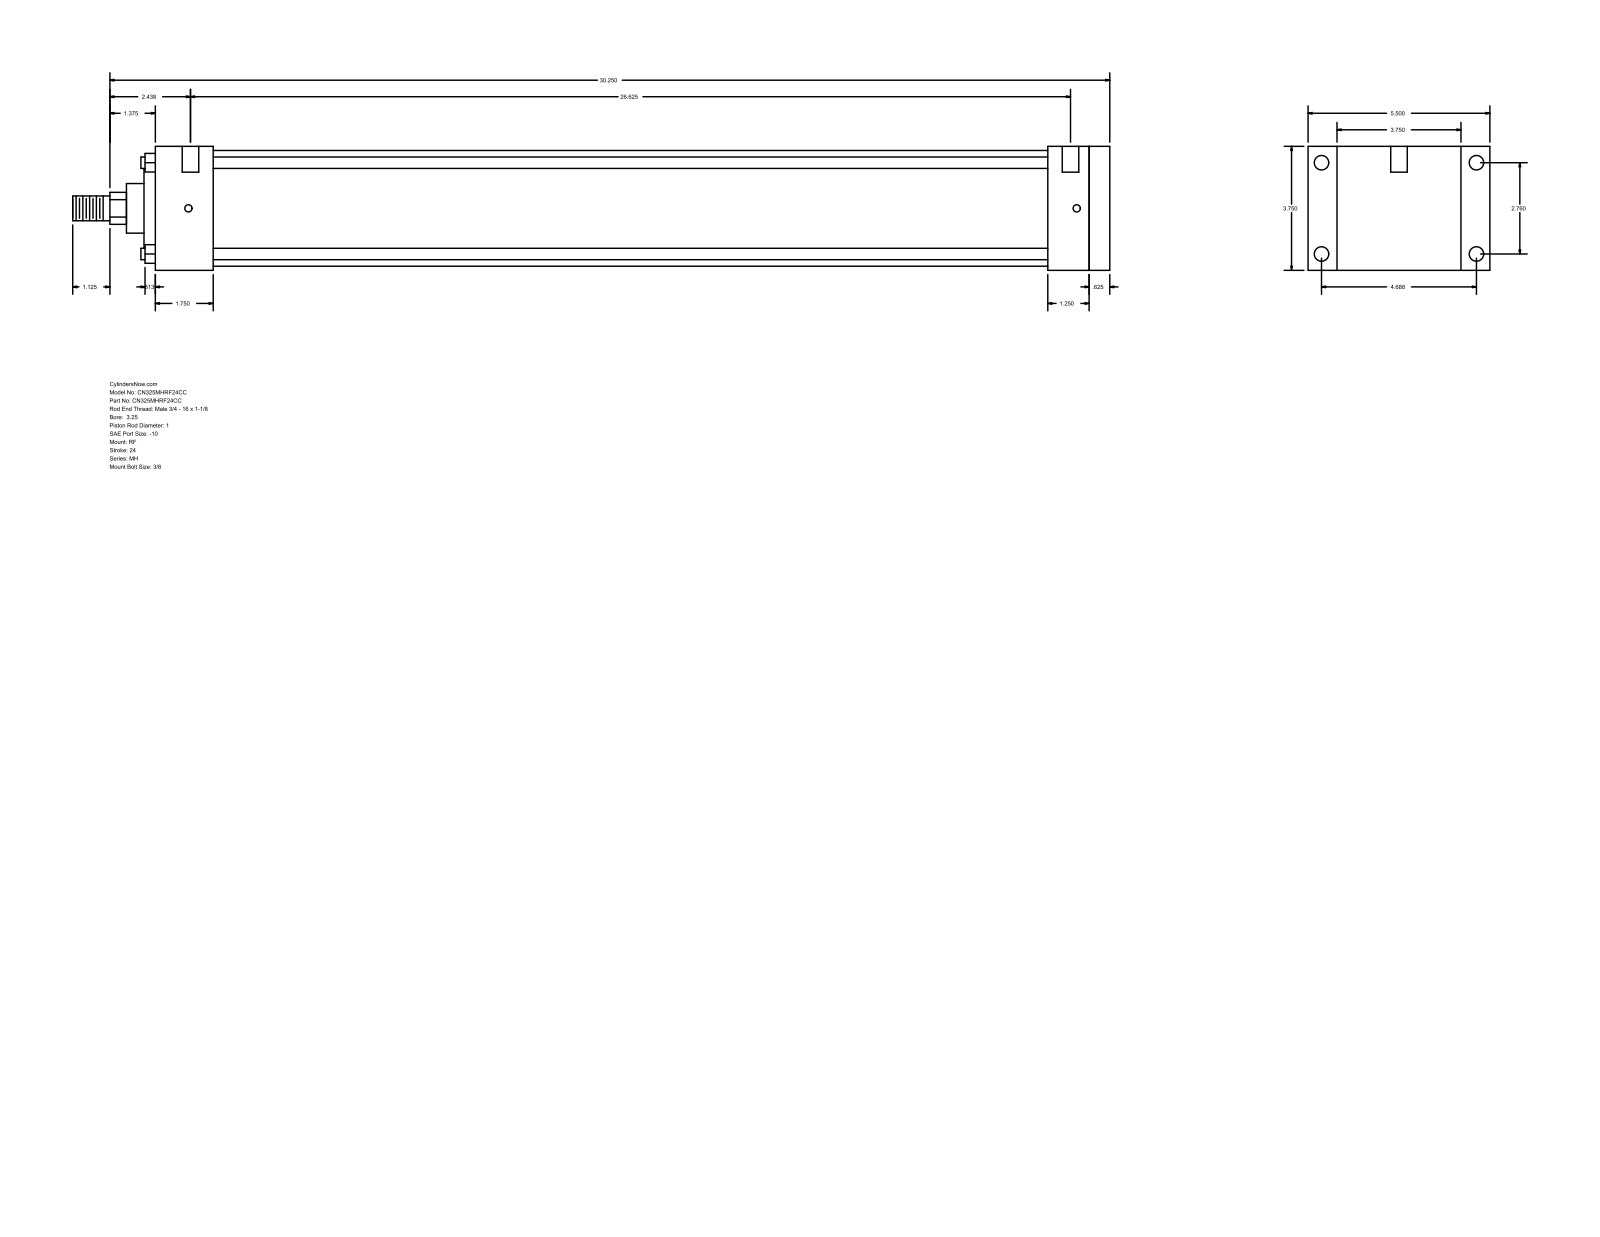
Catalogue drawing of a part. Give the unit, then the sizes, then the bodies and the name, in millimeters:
Units: millimetres
Overall size (bounding box): 796.92 × 139.7 × 95.25
Round holes (diameter × count): ⌀5.56 ×4, ⌀11.13 ×4, ⌀12.7 ×2
Round bosses / shafts (diameter × count): ⌀8.76 ×4, ⌀88.9 ×1, ⌀60.33 ×1, ⌀38.1 ×1, ⌀25.4 ×1, ⌀19.05 ×1
Partial cylindrical surfaces — rounded edges, fillets, slot ends (radius × count): R12.29 ×1
Main face-to-face distances: 95.24, 733.43, 717.56, 15.87, 22.23, 117.47, 44.46, 673.1, 688.97, 685.81
Hole centre spacings: 70.1, 119.06, 138.16, 682.62, 1.58, 4.76, 676.28, 677.86
Bodies: 0 solids, 94 faces (65 planar, 29 cylindrical, 0 other)
Part name (STEP PRODUCT): MH_RF__0325_1
STEP written by: GSSL Pune (CONFIG_CONTROL_DESIGN)
